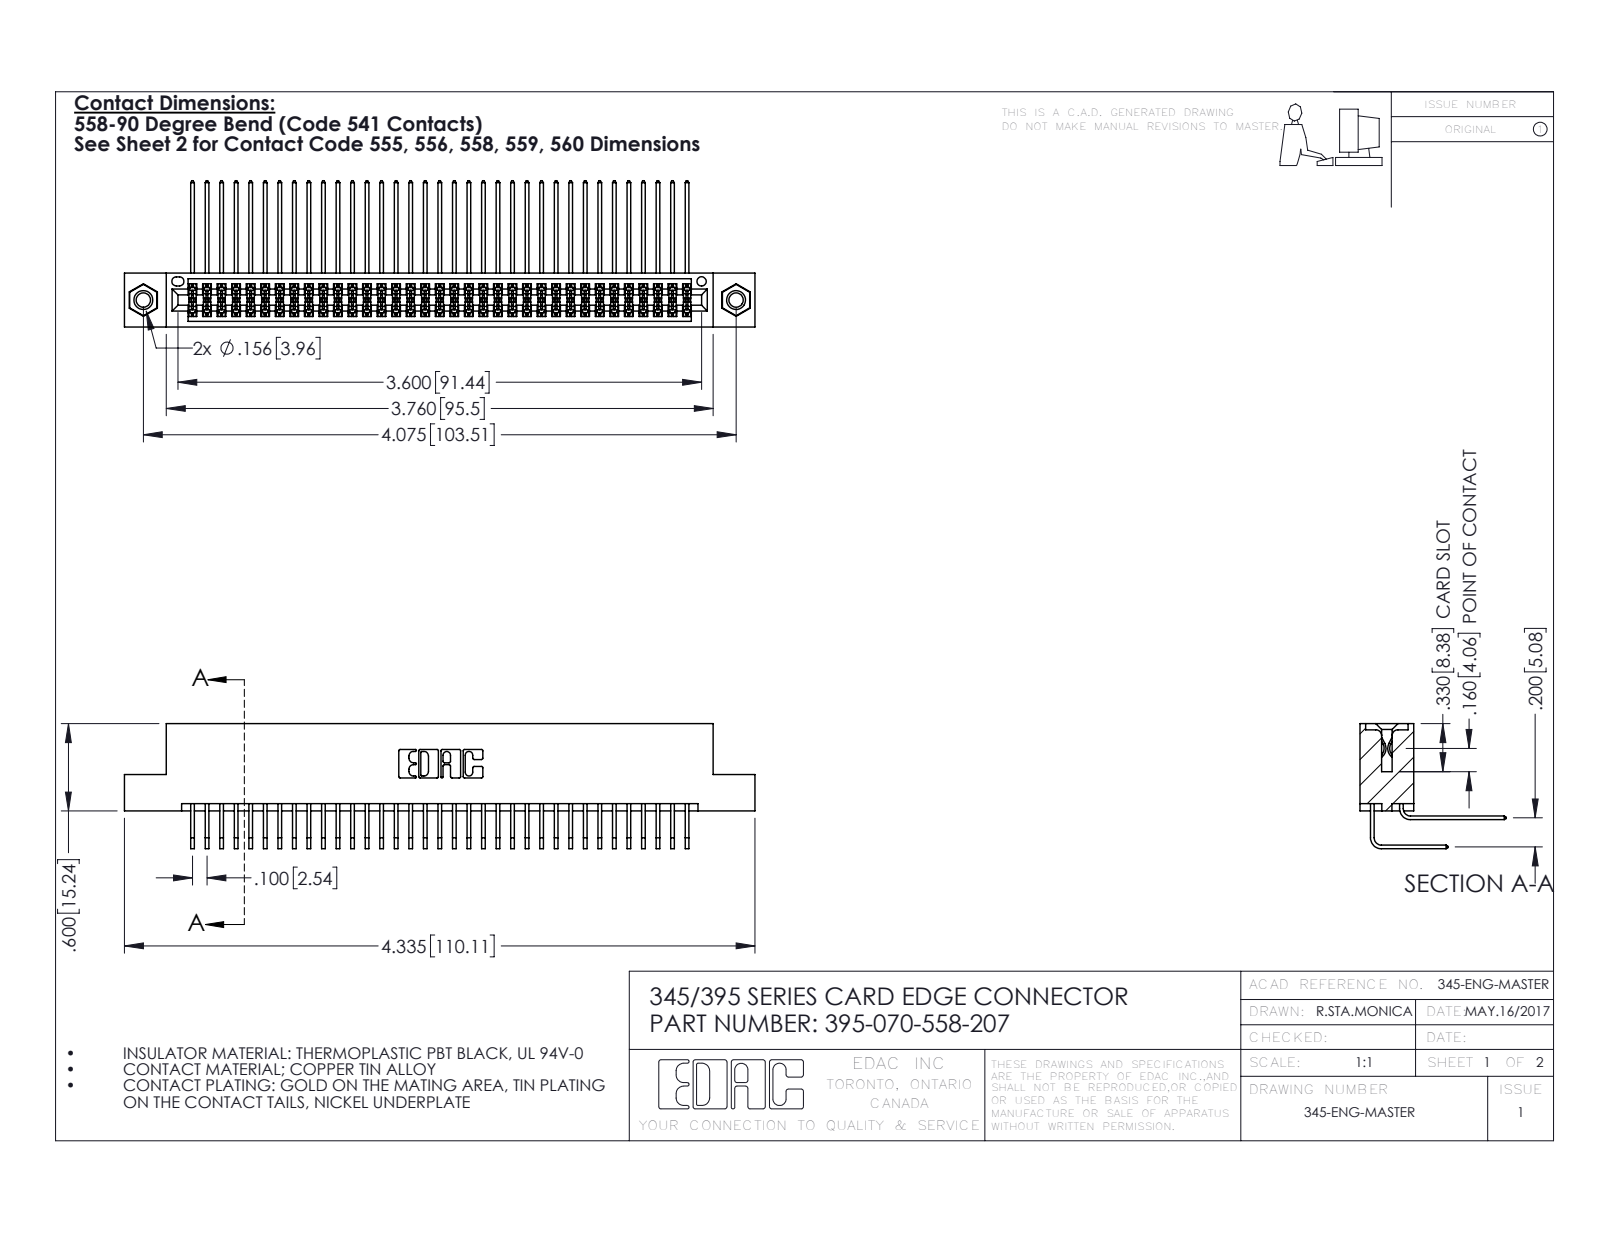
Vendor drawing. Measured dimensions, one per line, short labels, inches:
name: 345 Part_Flush Mounting Lugs - 0.156 Dia-TI; 345-250-001_345-250-005-103; 345-292-001_558 Tail - 2; 395-070-558-207 (+1 more)
written by: SolidWorks 2016 (CONFIG_CONTROL_DESIGN)
unit: in
bodies: 73 solids, 3826 faces (2562 planar, 1248 cylindrical, 16 other)
size: 4.335 × 1.005 × 0.859
volume: 0.673 in³; area: 28.03 in²
holes: 2× ⌀0.098, 2× ⌀0.125, 2× ⌀0.156, 1× ⌀0.064
bosses: 2× ⌀0.155
rounds: 106× R0.006, 22× R0.01, 6× R0.007, 6× R0.031, 3× R0.026, 2× R0.014, 2× R0.019, 2× R0.022
face distances: 0.072, 0.298, 0.2, 0.37, 0.098, 0.272, 0.025, 0.225, 0.025, 0.175
hole spacings: 0.27, 3.839, 4.075
